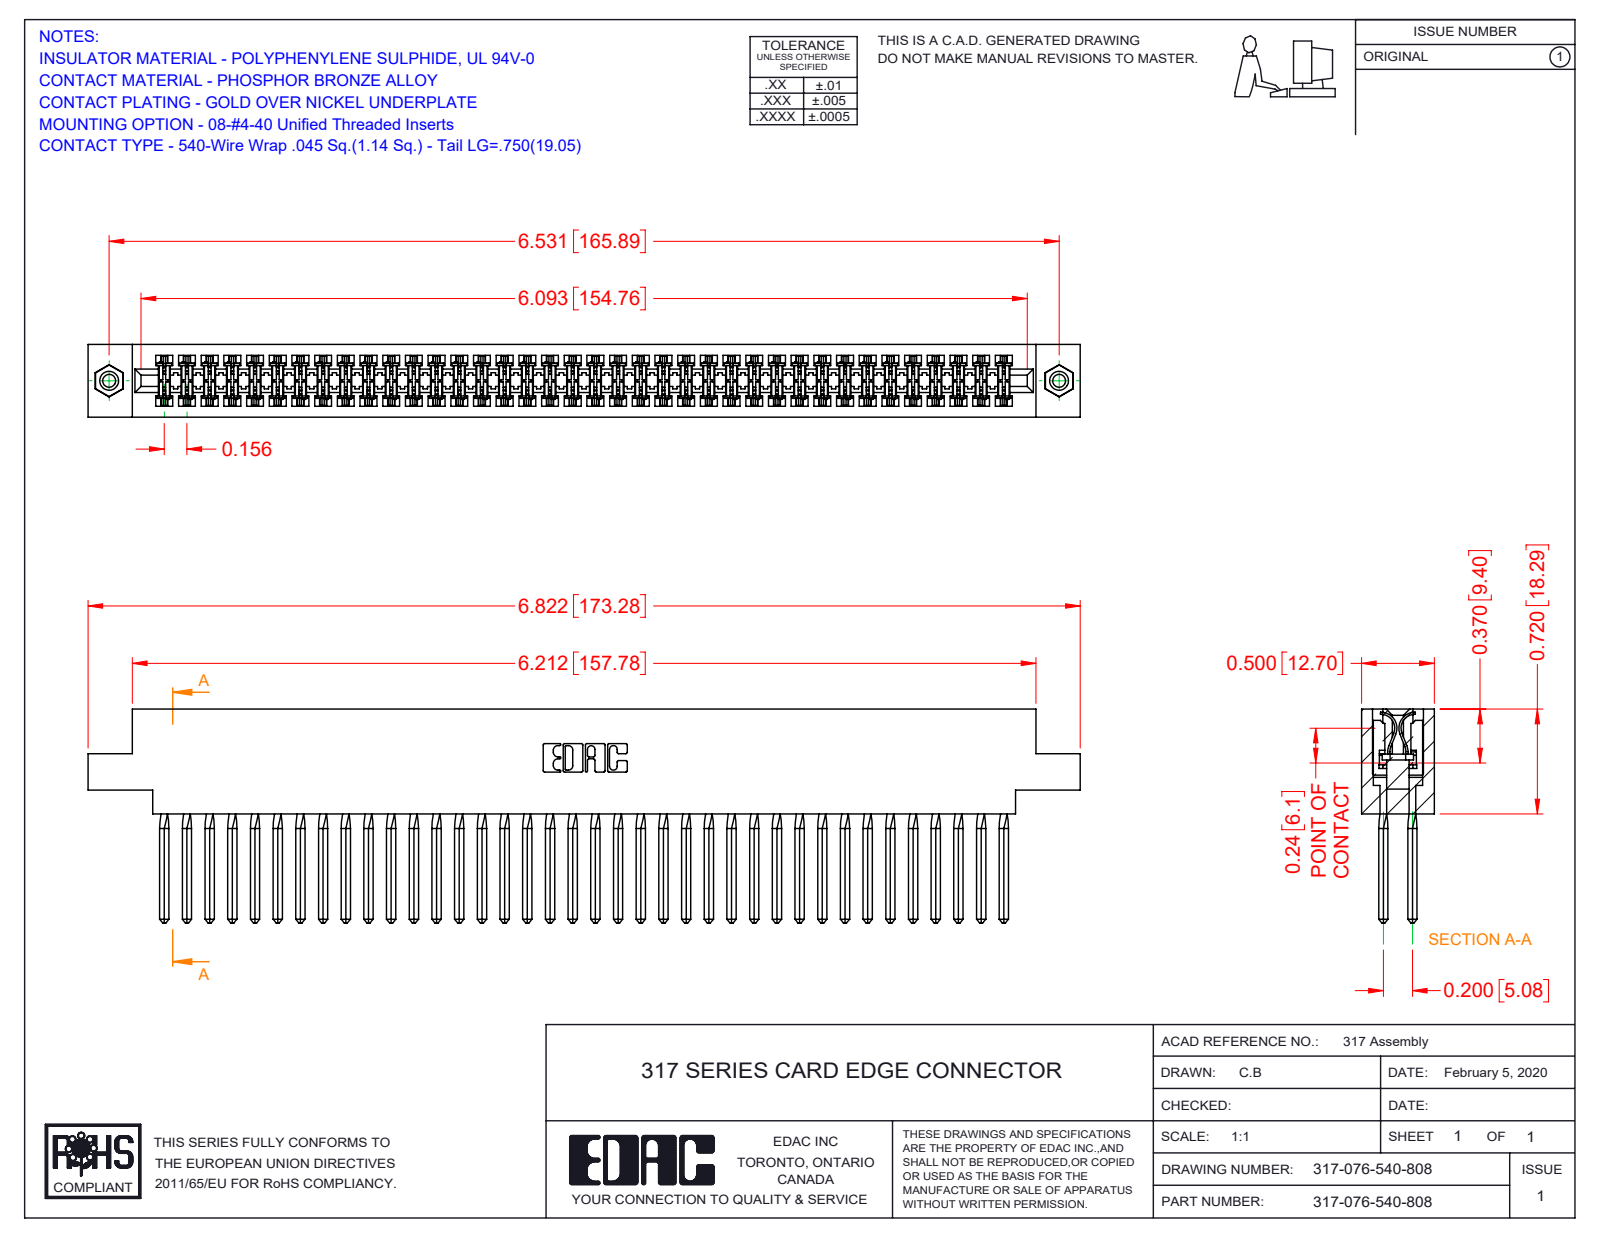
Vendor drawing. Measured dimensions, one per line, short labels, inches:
name: 345-250-001_345-250-003-102; 317-290-001_540; 317-076-540-878; 317 Part_.156 Dia - TI
written by: SolidWorks 2016 (CONFIG_CONTROL_DESIGN)
unit: in
bodies: 79 solids, 6926 faces (5638 planar, 968 cylindrical, 320 other)
size: 6.822 × 1.47 × 0.5
volume: 1.766 in³; area: 66.68 in²
holes: 2× ⌀0.089, 2× ⌀0.125, 2× ⌀0.156
bosses: 2× ⌀0.155
rounds: 152× R0.015, 22× R0.01, 6× R0.007, 6× R0.031, 3× R0.026, 2× R0.095, 2× R0.1, 2× R0.11
face distances: 0.5, 0.075, 0.425, 0.35, 0.195, 0.094, 0.11, 0.2, 0.115, 0.131
hole spacings: 6.531
